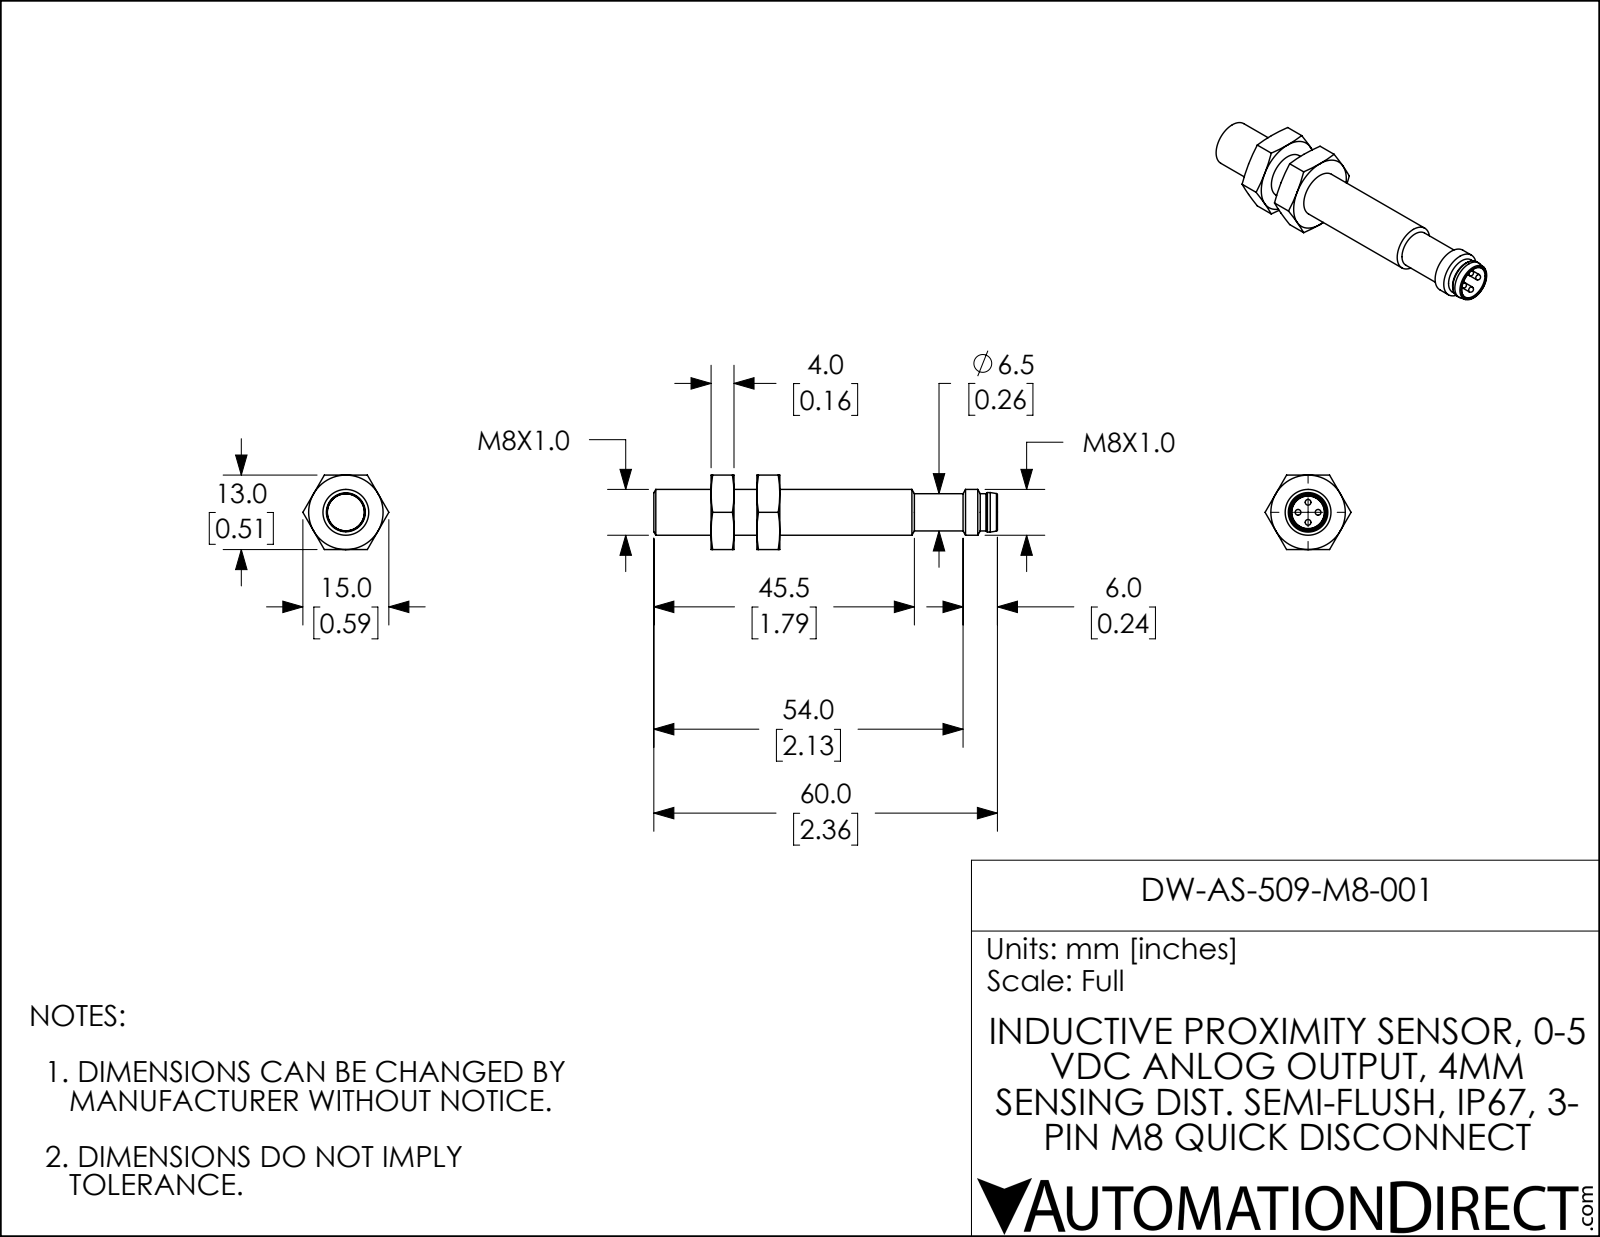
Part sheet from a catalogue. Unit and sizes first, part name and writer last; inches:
Units: inches
Overall size (bounding box): 2.362 × 0.315 × 0.315
Round holes (diameter × count): ⌀0.228 ×1
Round bosses / shafts (diameter × count): ⌀0.039 ×4, ⌀0.315 ×1, ⌀0.272 ×1, ⌀0.256 ×1, ⌀0.255 ×1
Main face-to-face distances: 2.165, 1.957, 0.209, 2.362, 0.406, 0.197, 1.953, 2.161, 2.358
Volume: 0.163 in³ · Surface area: 3.041 in²
Bodies: 5 solids, 48 faces (14 planar, 11 cylindrical, 23 other)
Part name (STEP PRODUCT): DW-AS-509-M8-001
STEP written by: SolidWorks 2018 (AUTOMOTIVE_DESIGN)
